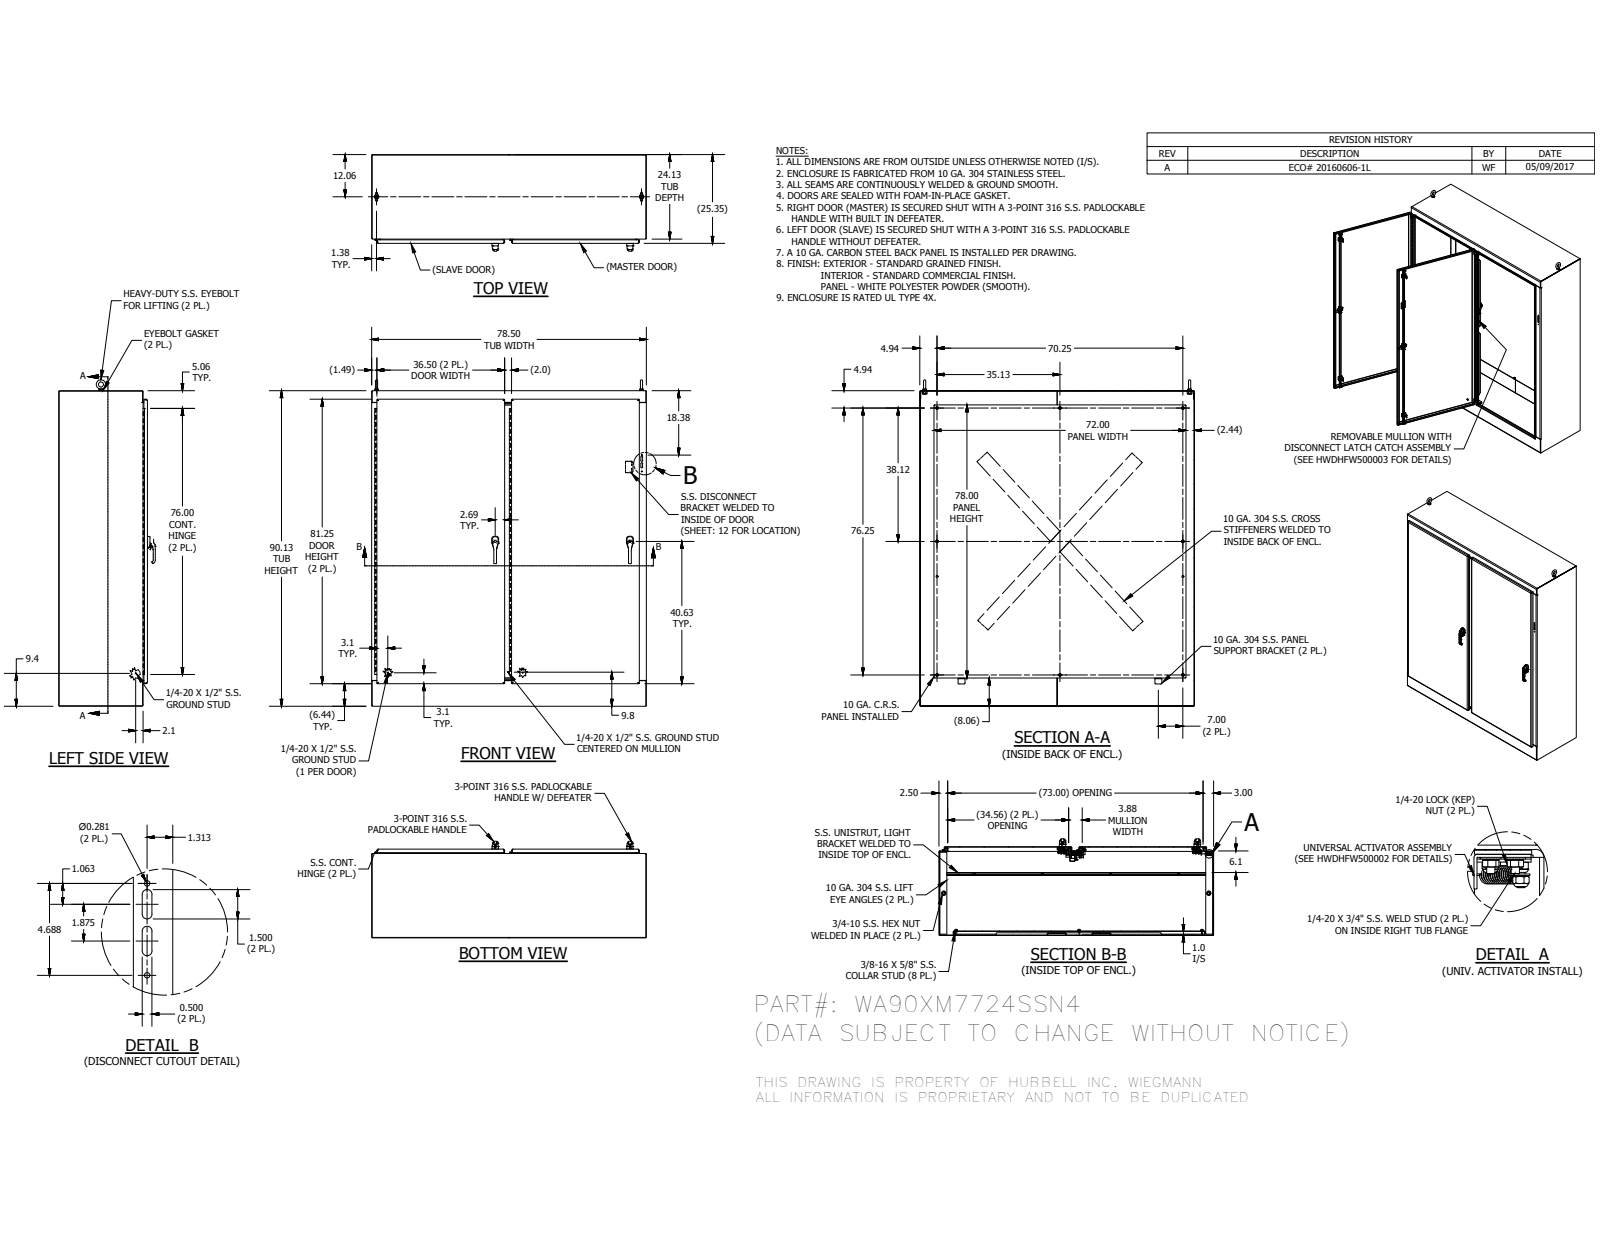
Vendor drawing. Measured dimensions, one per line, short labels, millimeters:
name: WA90XM24SSN4LS; WA90XM77SSN4HFB; WAXM7724SSN4TOP; WAXM7724SSN4BTM (+8 more)
written by: Autodesk Inventor 2016 (AUTOMOTIVE_DESIGN)
unit: mm
bodies: 258 solids, 10914 faces (5214 planar, 3572 cylindrical, 2128 other)
size: 2368.49 × 1993.9 × 701.02
volume: 70 910 000 mm³; area: 41 790 000 mm²
holes: 48× ⌀3.55, 18× ⌀9.52, 16× ⌀6.35, 10× ⌀14.29, 9× ⌀4.76, 8× ⌀3.45, 8× ⌀4.17, 8× ⌀4.83, 8× ⌀4.98, 8× ⌀5.1, 8× ⌀6.65, 8× ⌀7.33
bosses: 18× ⌀8.38, 18× ⌀6.35, 13× ⌀15.88, 12× ⌀8.56, 11× ⌀9.52, 9× ⌀14.29, 8× ⌀7.11, 8× ⌀6.02
rounds: 358× R0.5, 222× R0.3, 192× R0.51, 47× R3.17, 42× R0.47, 36× R1.59, 31× R6.35, 28× R1.27
face distances: 3.4, 3.41, 640.5, 637.1, 25.4, 643.9, 28.8, 615.1, 32.21, 28.81
hole spacings: 0.45, 973.57, 973.64, 973.5, 973.35, 973.42, 973.79, 1829.12
